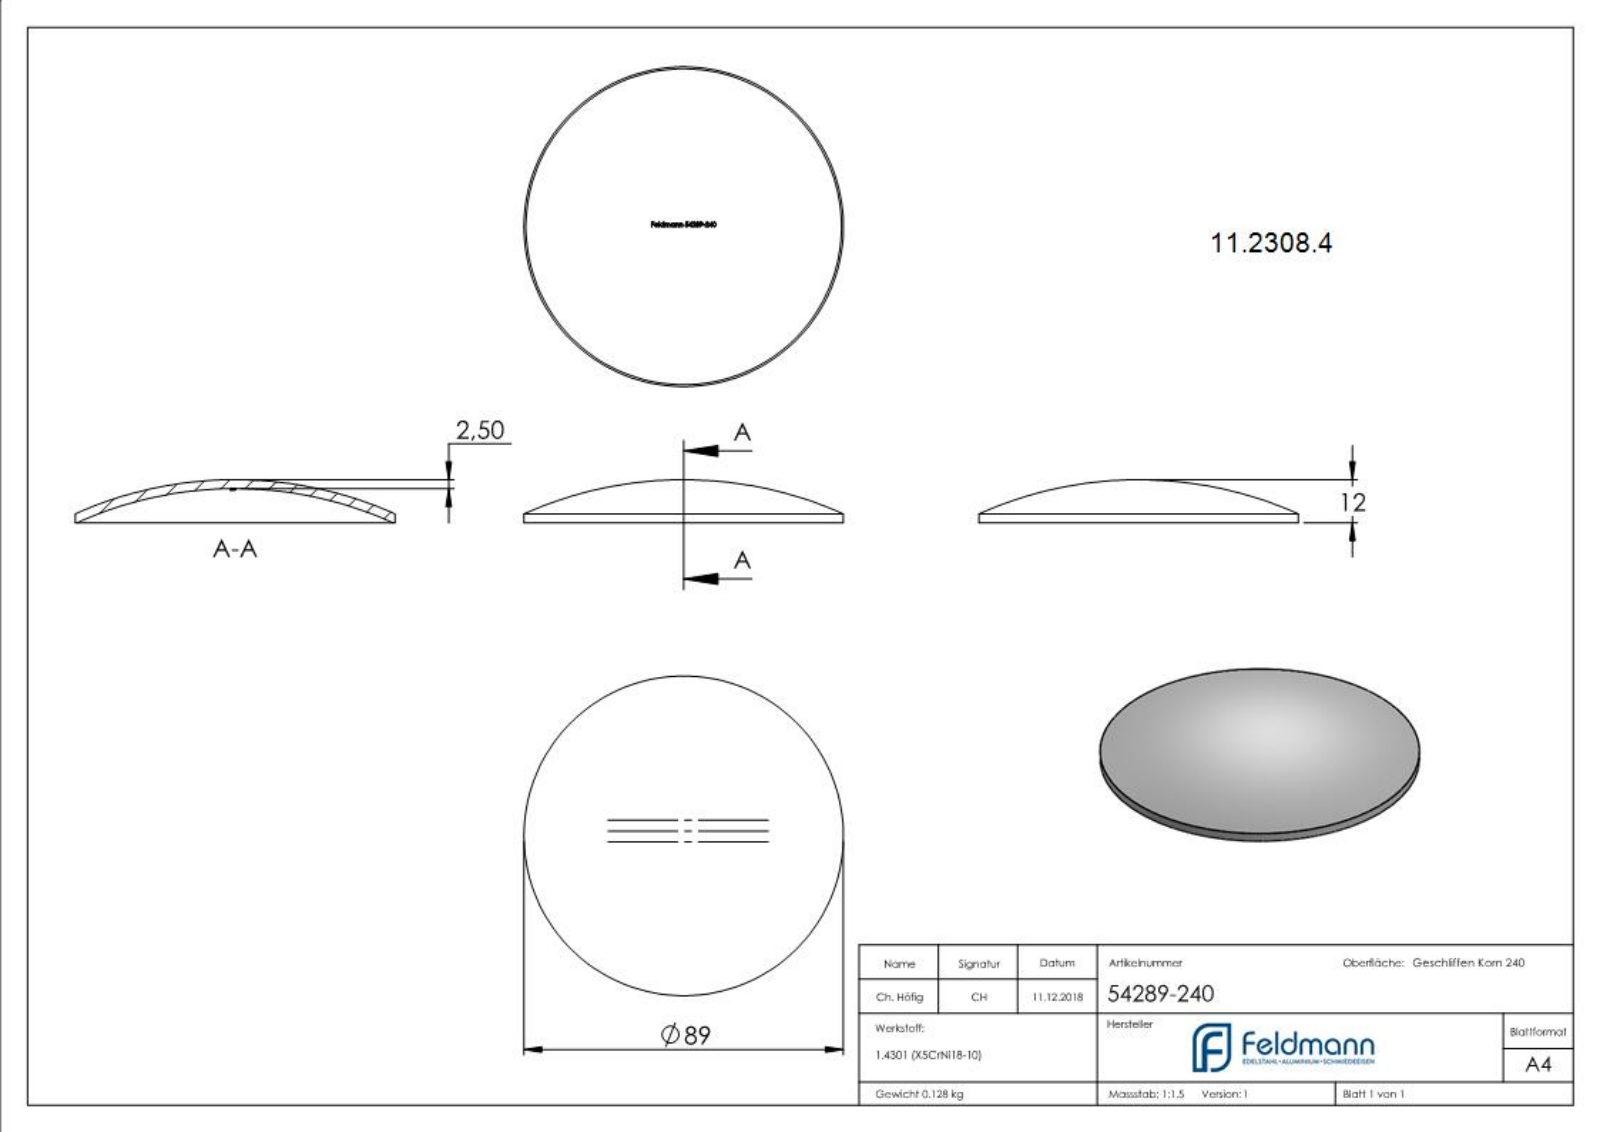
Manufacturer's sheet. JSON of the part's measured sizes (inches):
{"part_name": "54289-240", "step_written_by": "SolidWorks 2015 (CONFIG_CONTROL_DESIGN)", "units": "inches", "bodies": {"solids": 1, "faces": 254, "planar": 106, "cylindrical": 2, "other": 146}, "overall_size": [3.504, 3.504, 0.472], "volume_in3": 0.992, "surface_area_in2": 21.26, "round_bosses_or_shafts": [[3.504, 1]], "face_to_face_distances": [0.017, 0.117, 0.015, 0.185, 0.052, 0.035, 0.576, 0.302, 0.431, 0.05]}
